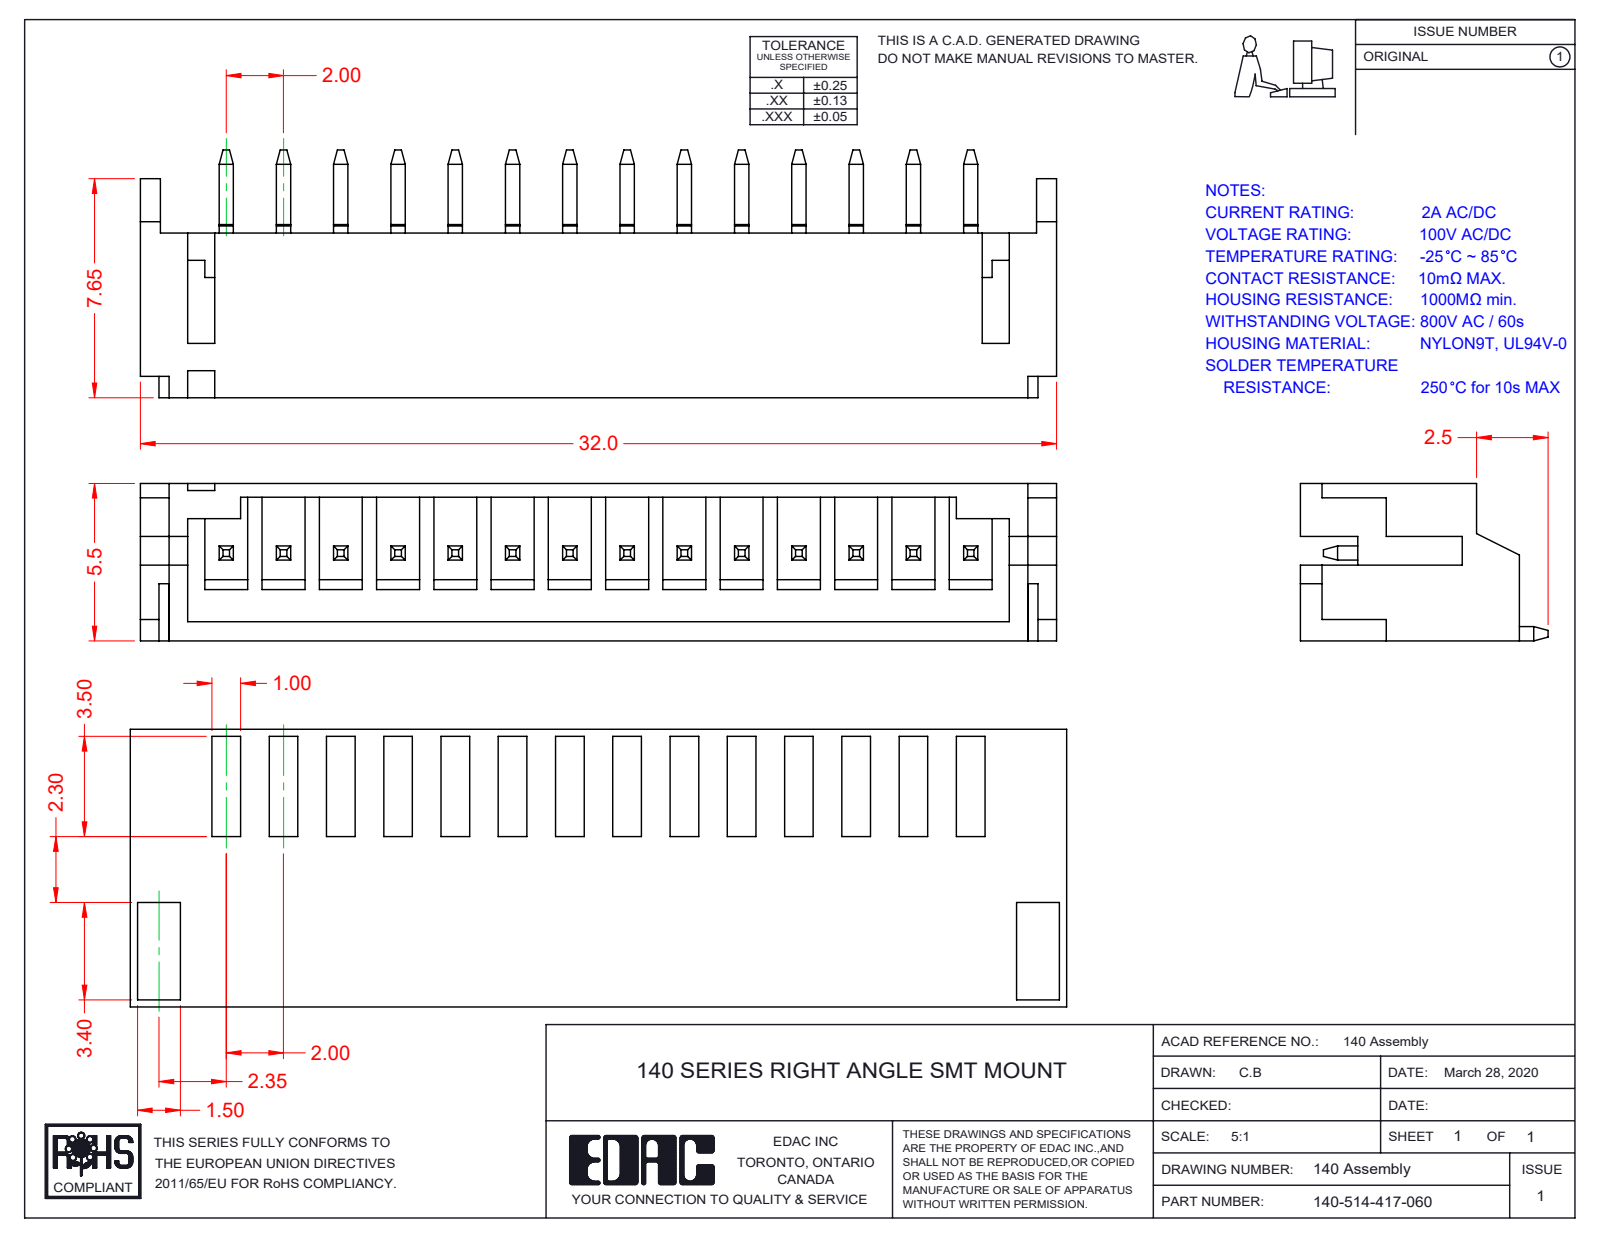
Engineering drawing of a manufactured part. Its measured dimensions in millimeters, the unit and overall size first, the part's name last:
Units: millimetres
Overall size (bounding box): 32 × 8.65 × 5.5
Partial cylindrical surfaces — rounded edges, fillets, slot ends (radius × count): R0.55 ×2
Main face-to-face distances: 5.5, 0.67, 0.65, 4.83, 4.35, 5.02, 0.48, 0.5, 0.95, 0.9
Volume: 420 mm³ · Surface area: 1 608 mm²
Bodies: 17 solids, 724 faces (668 planar, 56 cylindrical, 0 other)
Part name (STEP PRODUCT): 140-514-417-060; RA SMT Pad; RA SMT Contact; RA SMT Housing_514
STEP written by: SolidWorks 2016 (CONFIG_CONTROL_DESIGN)
